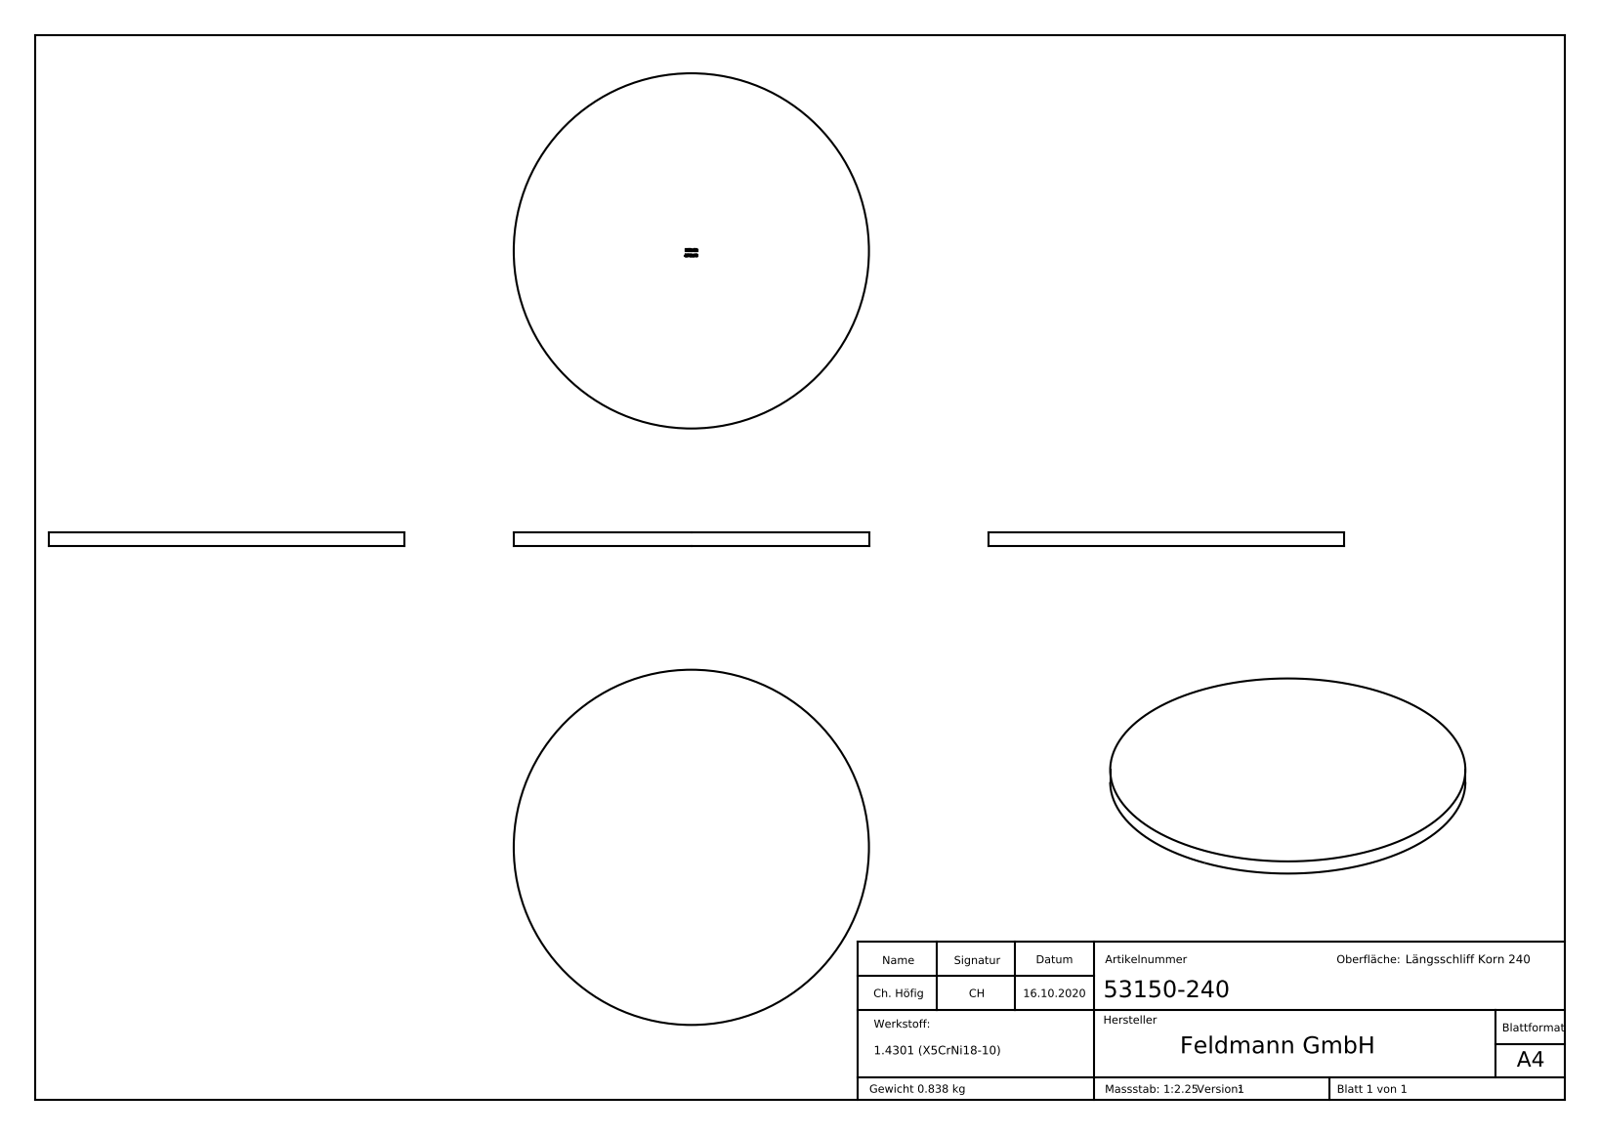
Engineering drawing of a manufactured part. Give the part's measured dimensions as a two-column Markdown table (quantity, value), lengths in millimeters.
| quantity | value |
| --- | --- |
| part name | 53150-240 |
| STEP written by | SolidWorks 2018 (CONFIG_CONTROL_DESIGN) |
| units | millimeters |
| bodies | 1 solid, 227 faces (123 planar, 2 cylindrical, 102 other) |
| overall size | 150 × 150 × 6 |
| volume | 106 029 mm³ |
| surface area | 38 176 mm² |
| round bosses / shafts (diameter × count) | 150 × 1 |
| main face-to-face distances | 6, 5.9, 1.78, 0.83, 0.76, 0.53, 2.45, 2.61, 0.79, 2.41 |
